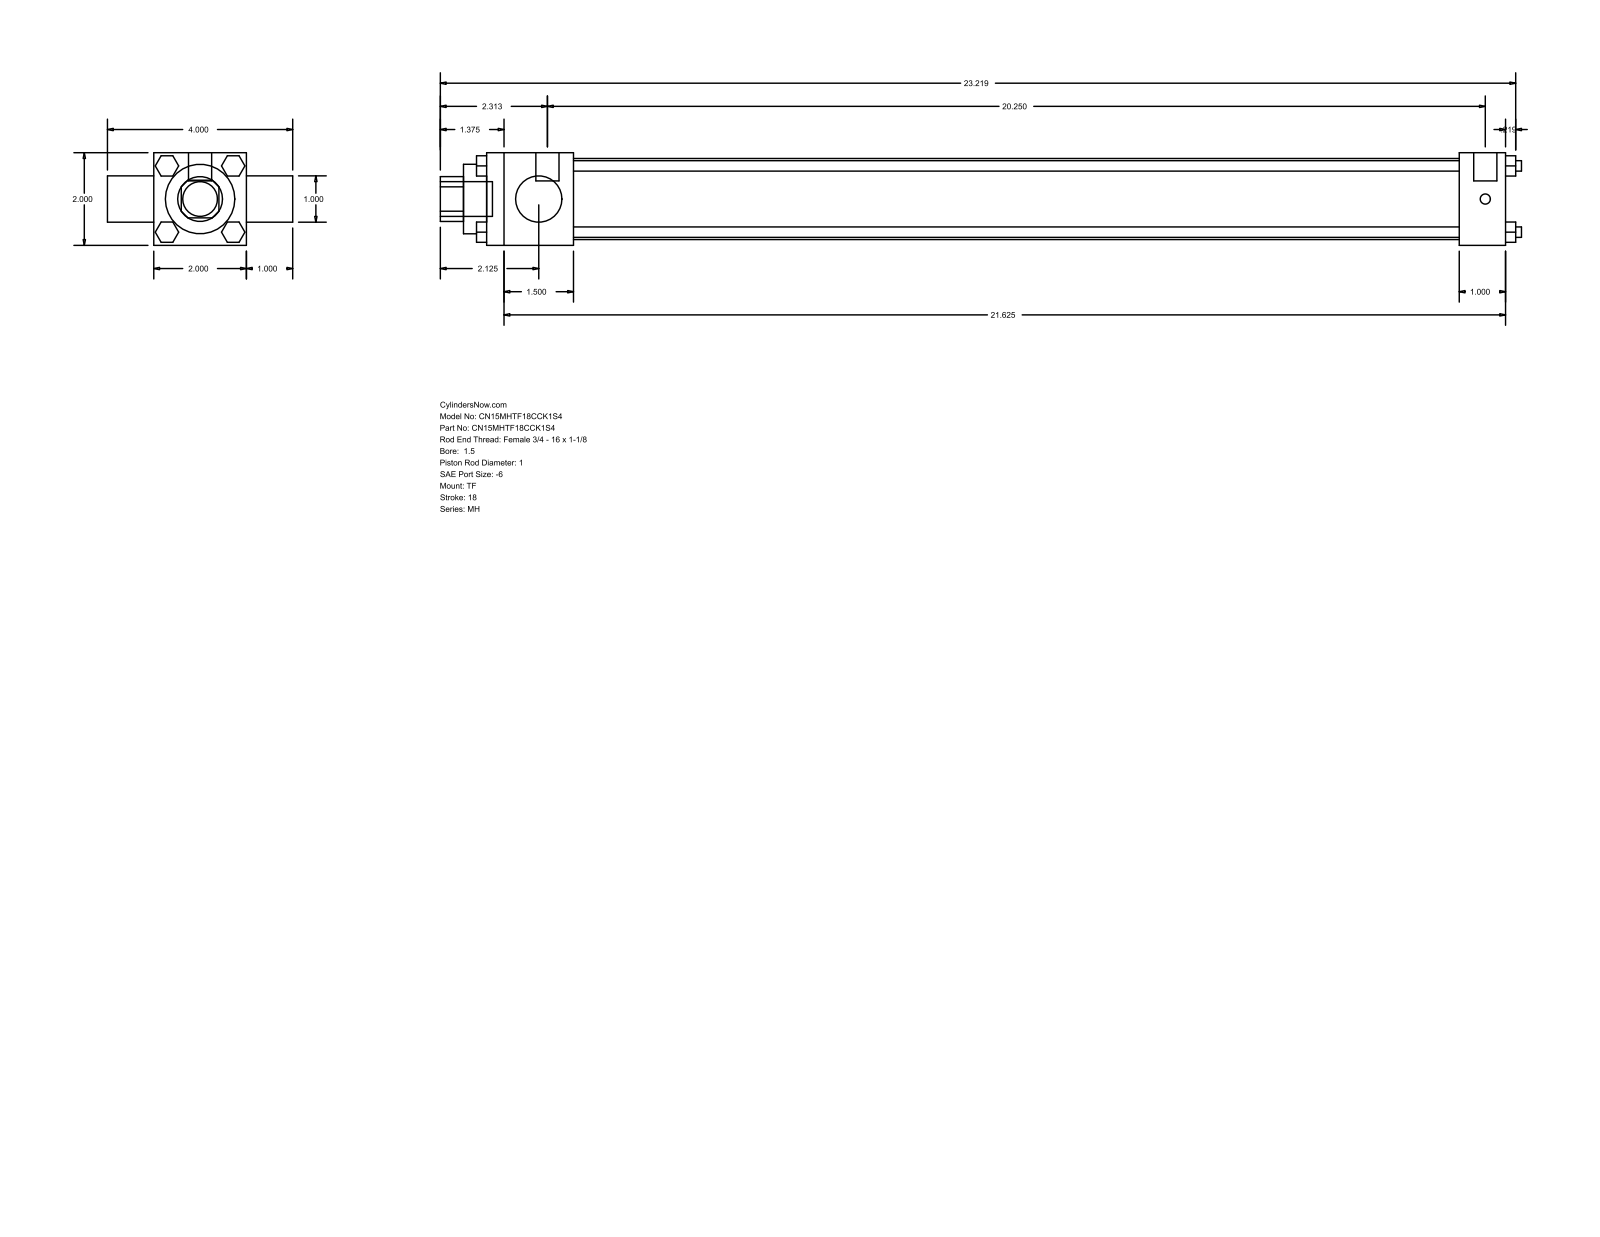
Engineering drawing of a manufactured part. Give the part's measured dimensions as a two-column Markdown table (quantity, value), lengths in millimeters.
| quantity | value |
| --- | --- |
| part name | MH_TF__0150_1 |
| STEP written by | GSSL Pune (CONFIG_CONTROL_DESIGN) |
| units | millimeters |
| bodies | 0 solids, 120 faces (92 planar, 28 cylindrical, 0 other) |
| overall size | 592.93 × 101.6 × 50.8 |
| round holes (diameter × count) | 25.4 × 2, 38.1 × 1, 44.45 × 1 |
| round bosses / shafts (diameter × count) | 5.71 × 4, 5.56 × 3, 12.7 × 2, 19.05 × 1 |
| partial cylindrical surfaces (radius × count) | 12.29 × 1 |
| main face-to-face distances | 50.8, 25.4, 558.8, 76.2, 47.63, 511.17, 533.4, 485.77, 564.36, 12.7 |
